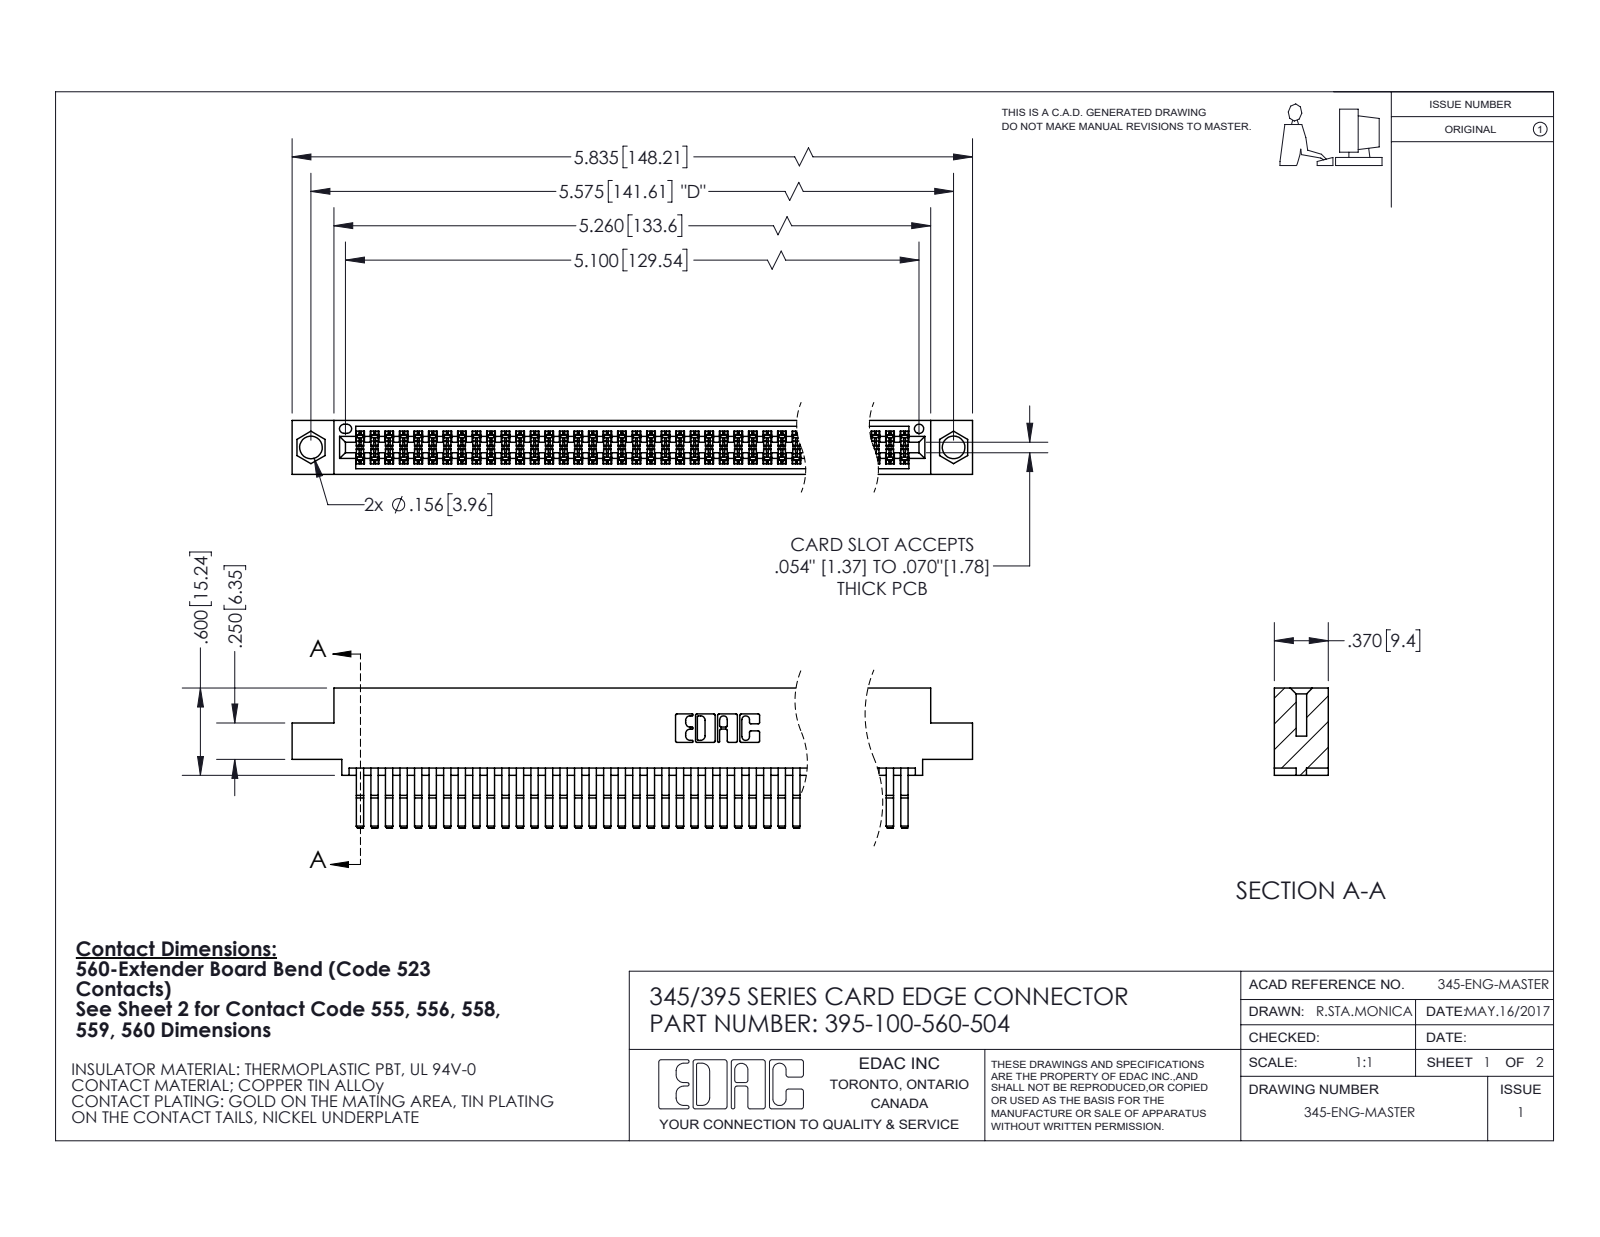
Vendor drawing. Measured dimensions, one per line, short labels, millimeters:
name: 395-100-560-504; 345 Part_0.110 Offset - 0.156 Dia-TI; 345-292-001_560 Tail
written by: SolidWorks 2020 (CONFIG_CONTROL_DESIGN)
unit: mm
bodies: 101 solids, 5344 faces (3398 planar, 1946 cylindrical, 0 other)
size: 148.2 × 24.4 × 9.4
volume: 14 900 mm³; area: 23 880 mm²
holes: 2× ⌀4, 1× ⌀1.6
rounds: 150× R0.2, 22× R0.3, 6× R0.2, 6× R0.8, 3× R0.7, 2× R0.3, 2× R0.4, 2× R0.5
face distances: 0.6, 7.6, 1.8, 9.4, 5.1, 2.5, 6.9, 5.7, 4.4, 3.8
hole spacings: 6.9, 135.6, 141.6
